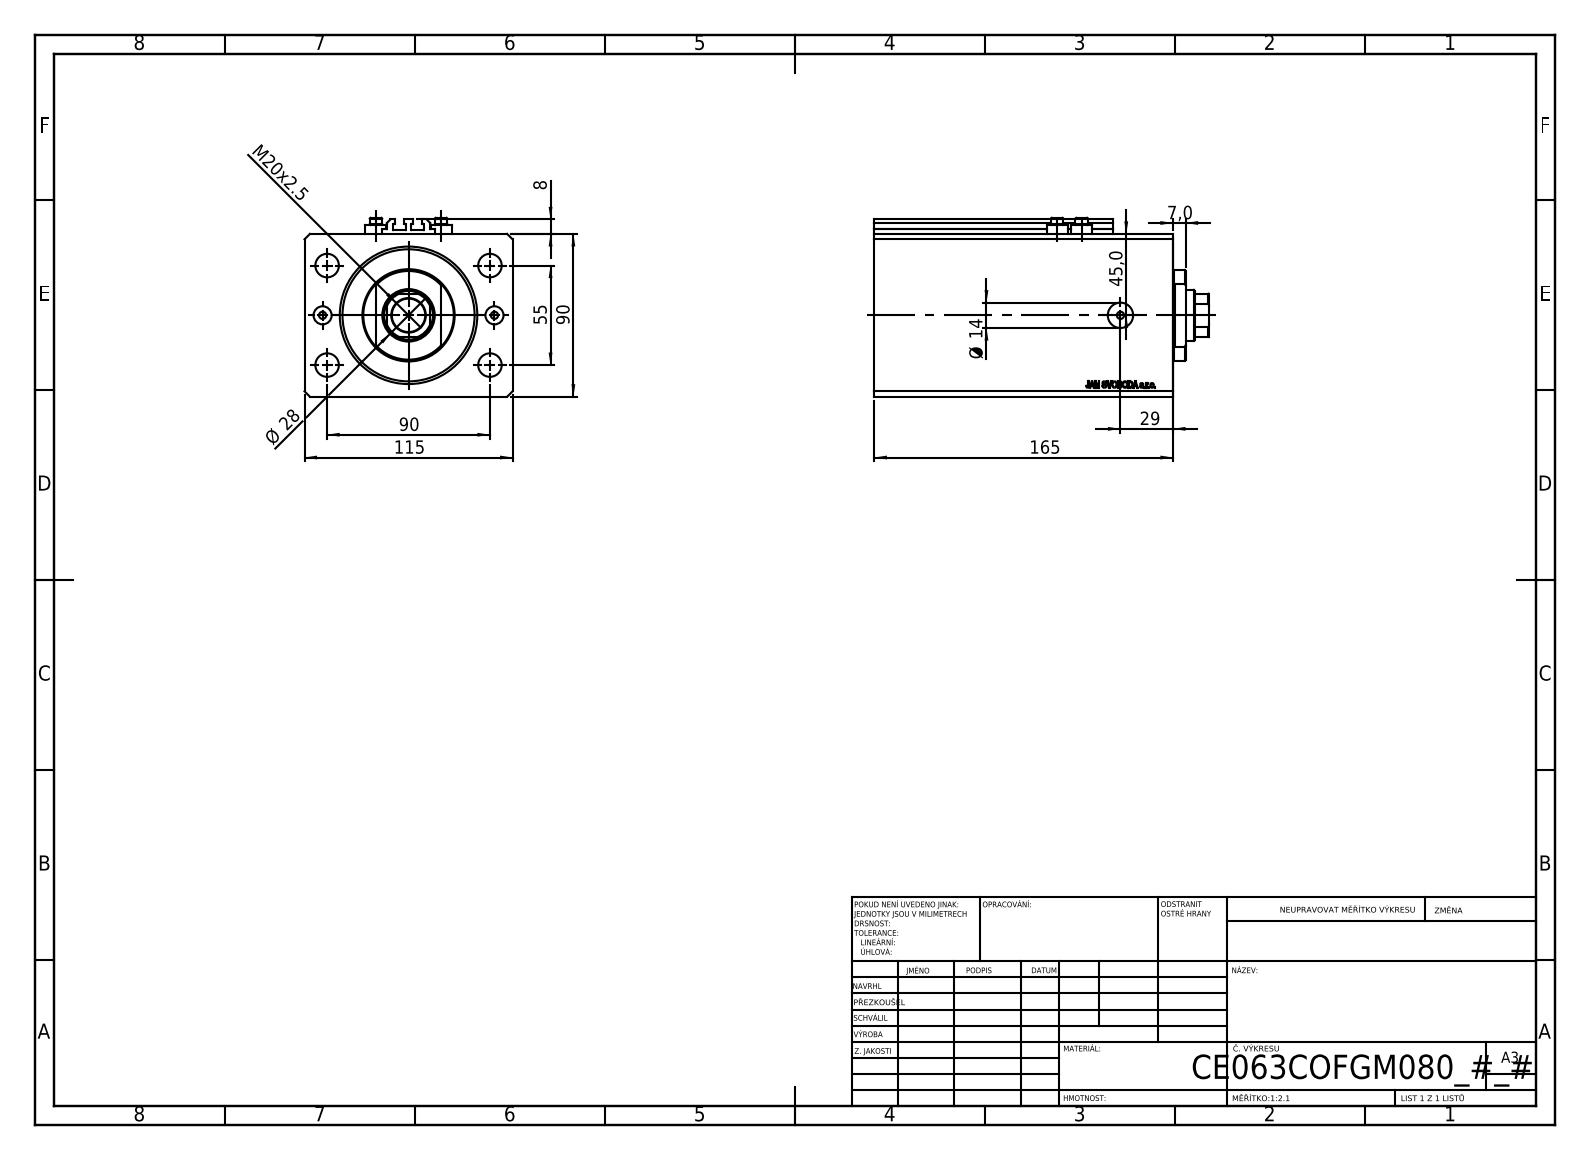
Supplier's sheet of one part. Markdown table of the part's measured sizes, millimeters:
| quantity | value |
| --- | --- |
| part name | V250CE_VC_C; V250CE_C_VCP; V250CE_C_Body; ALLEN BOLT V250CE |
| STEP written by | SolidWorks 2019 (CONFIG_CONTROL_DESIGN) |
| units | millimeters |
| bodies | 8 solids, 1034 faces (504 planar, 86 cylindrical, 444 other) |
| overall size | 185 × 115 × 99 |
| volume | 1 442 000 mm³ |
| surface area | 204 842 mm² |
| round holes (diameter × count) | 4 × 8, 13 × 4, 10 × 2, 14 × 2, 18.5 × 1, 28 × 1, 63 × 1, 76 × 1 |
| round bosses / shafts (diameter × count) | 11.6 × 4, 7 × 4, 50 × 1 |
| partial cylindrical surfaces (radius × count) | 0.2 × 10, 13.5 × 1 |
| main face-to-face distances | 90, 115, 165, 17.9, 147.1, 20, 145, 127.1, 65, 80 |
| hole center spacings | 27.61, 52.74, 96.5, 13.6, 36, 38.48, 47.5, 55 |
